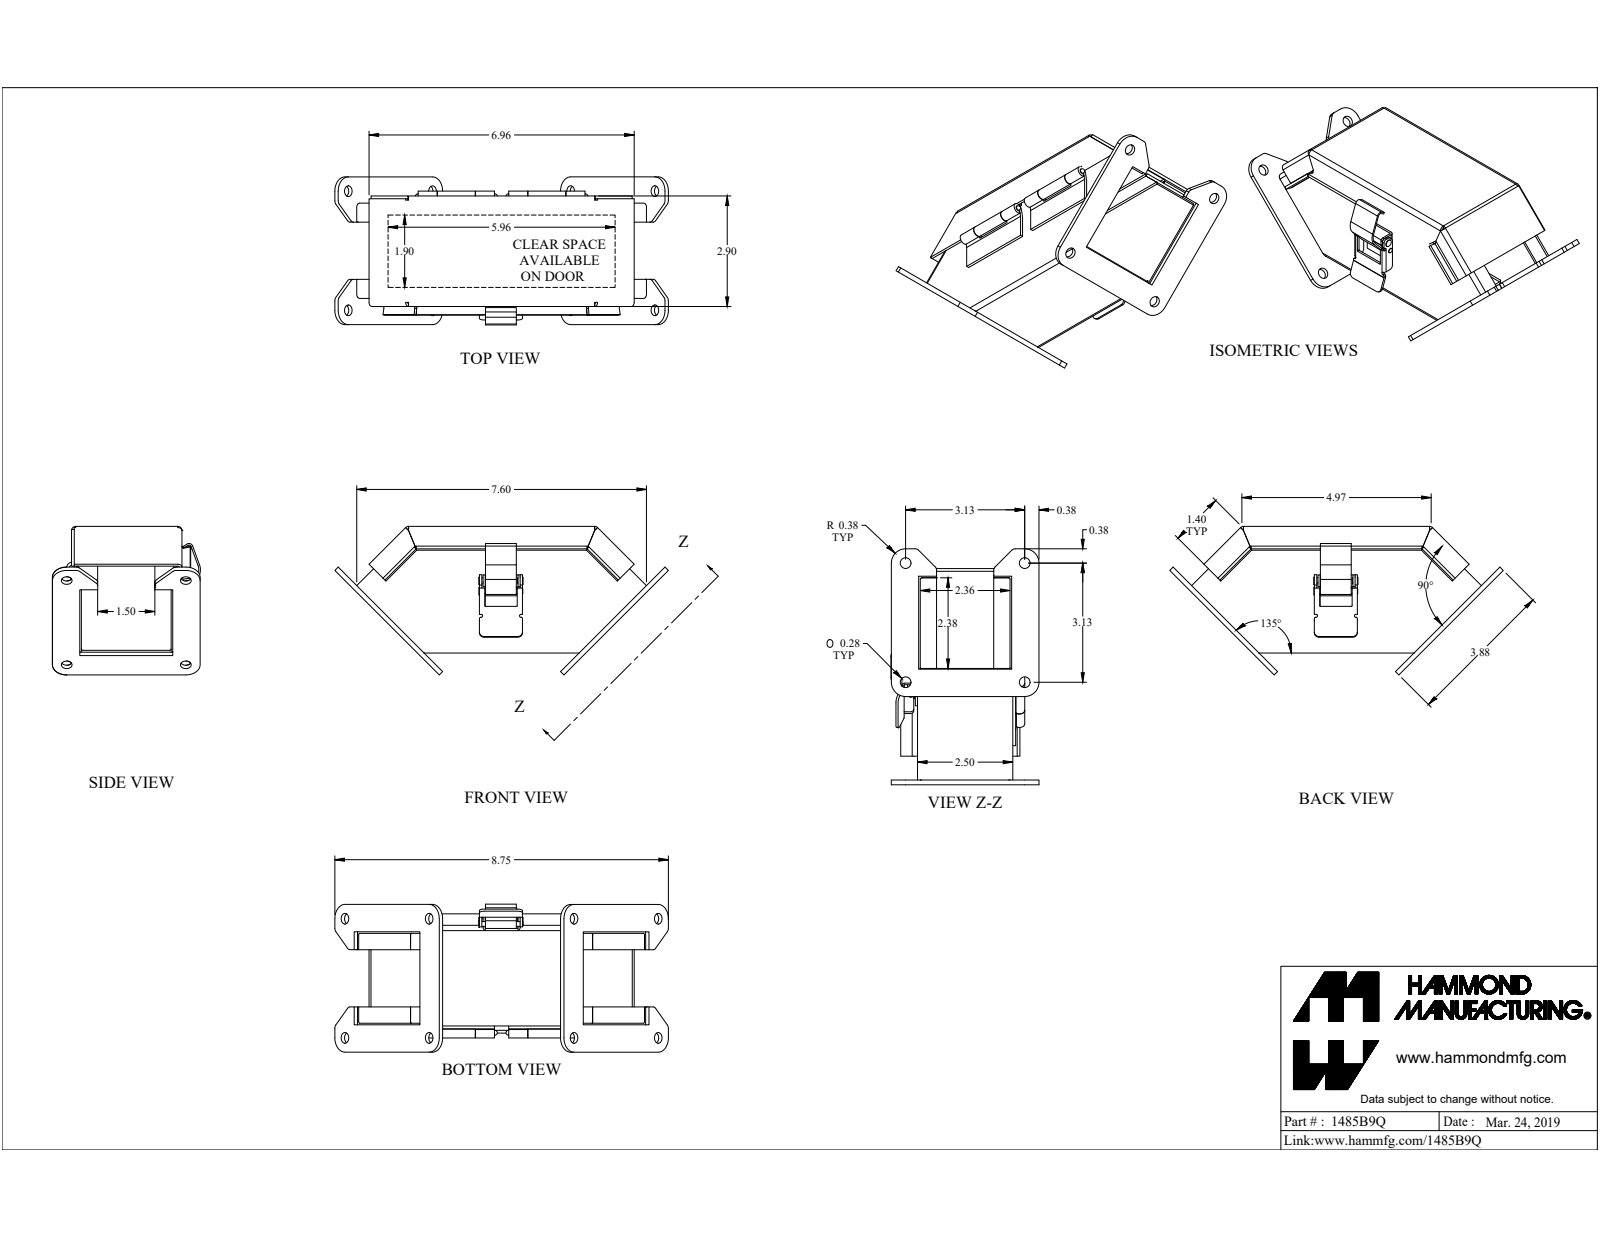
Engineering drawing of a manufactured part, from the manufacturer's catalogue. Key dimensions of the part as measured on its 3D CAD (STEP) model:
Part name (STEP PRODUCT): 1485B9Q
STEP written by: SolidWorks 2019 (CONFIG_CONTROL_DESIGN)
Units: inches
Bodies: 13 solids, 372 faces (228 planar, 124 cylindrical, 20 other)
Overall size (bounding box): 8.751 × 3.896 × 3.883
Volume: 8.933 in³ · Surface area: 243.2 in²
Round holes (diameter × count): ⌀0.281 ×8, ⌀0.125 ×1, ⌀0.13 ×1, ⌀0.164 ×1
Round bosses / shafts (diameter × count): ⌀0.187 ×2, ⌀0.275 ×1, ⌀0.156 ×1, ⌀0.125 ×1, ⌀0.125 ×1
Partial cylindrical surfaces — rounded edges, fillets, slot ends (radius × count): R0.036 ×17, R0.108 ×17, R0.125 ×11, R0.375 ×8, R0.016 ×7, R0.035 ×3, R0.039 ×3, R0.076 ×3
Main face-to-face distances: 0.072, 2.428, 3.25, 2.5, 2.356, 0.125, 2.615, 0.187, 3.322, 3.178
Hole centre spacings: 3.125, 4.419, 0.285, 2.919, 2.948
